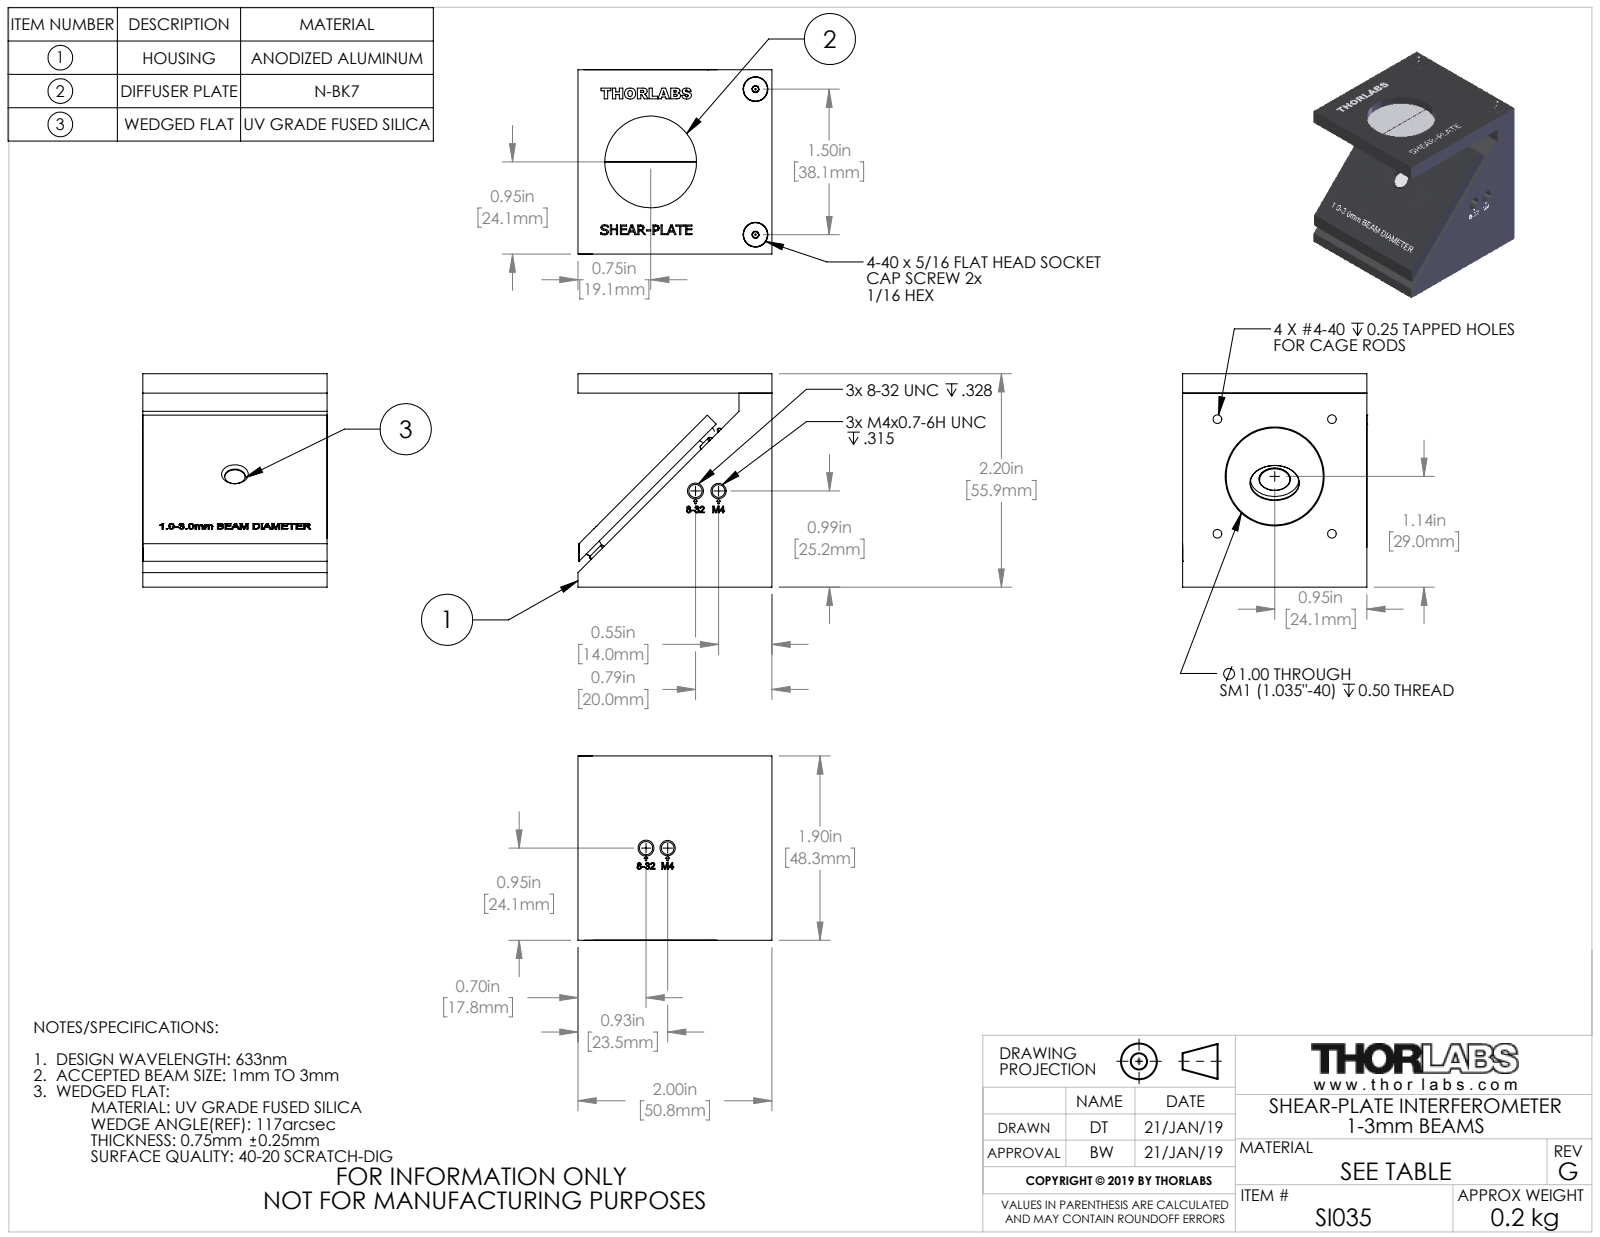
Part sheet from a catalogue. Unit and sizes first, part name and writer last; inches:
Units: inches
Overall size (bounding box): 2.2 × 2 × 1.9
Round holes (diameter × count): ⌀0.089 ×6, ⌀0.063 ×3, ⌀0.124 ×3, ⌀0.136 ×3, ⌀0.142 ×3, ⌀0.164 ×3, ⌀0.187 ×3, ⌀0.129 ×2, ⌀0.13 ×2, ⌀0.157 ×2, ⌀0.213 ×1, ⌀0.315 ×1
Round bosses / shafts (diameter × count): ⌀0.094 ×16, ⌀0.063 ×6, ⌀0.125 ×2, ⌀0.112 ×2, ⌀1 ×1, ⌀0.313 ×1, ⌀0.125 ×1
Partial cylindrical surfaces — rounded edges, fillets, slot ends (radius × count): R0.031 ×12, R0.047 ×4
Main face-to-face distances: 2, 0.128, 2.2, 0.2, 1.9, 0.076, 0.204, 0.343, 0.215, 0.139
Hole centre spacings: 0.835, 1.181, 1.793, 0.998, 1, 1.176, 1.316, 1.355
Volume: 4.534 in³ · Surface area: 41.93 in²
Bodies: 19 solids, 1135 faces (544 planar, 194 cylindrical, 397 other)
Part name (STEP PRODUCT): 16648-E0W
STEP written by: SolidWorks 2018 (CONFIG_CONTROL_DESIGN)
